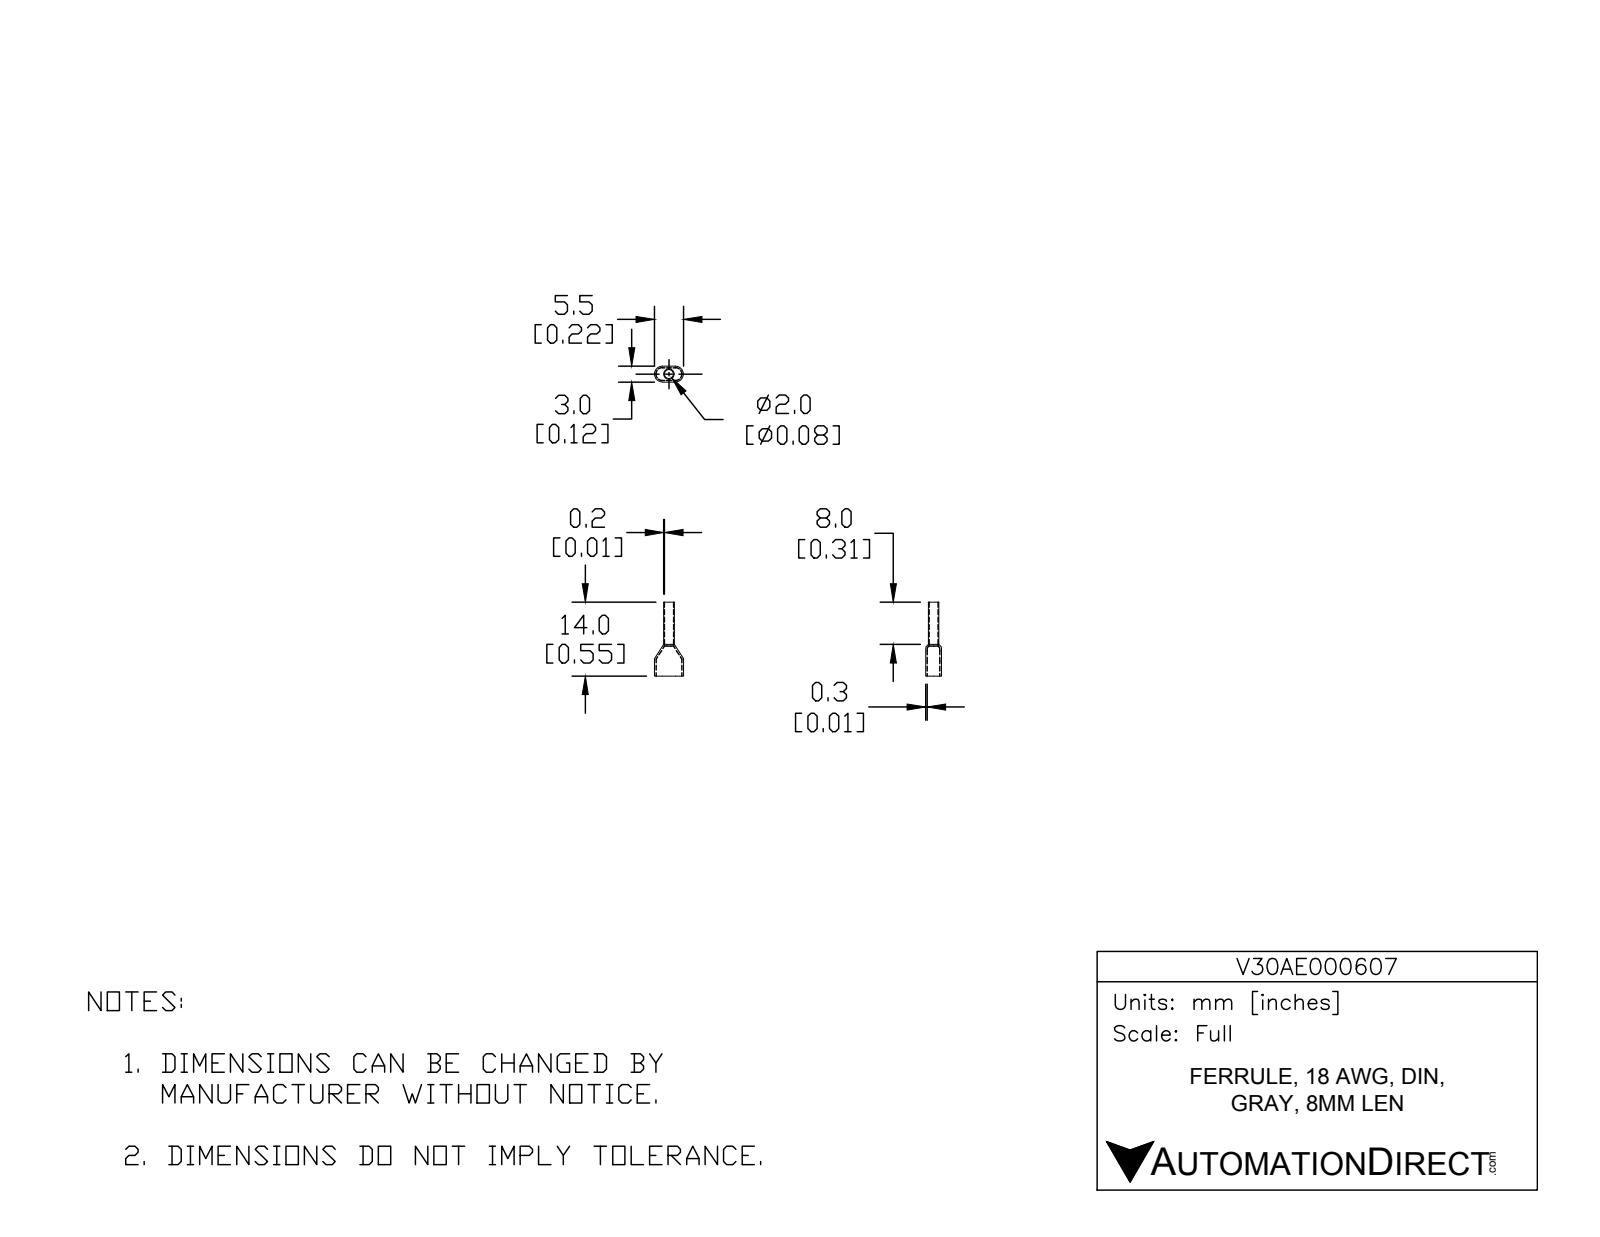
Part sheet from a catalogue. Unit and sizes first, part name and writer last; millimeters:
Units: millimetres
Overall size (bounding box): 14 × 5.5 × 3
Round holes (diameter × count): ⌀1.7 ×1
Round bosses / shafts (diameter × count): ⌀2 ×1
Partial cylindrical surfaces — rounded edges, fillets, slot ends (radius × count): R1.2 ×4, R1.5 ×4
Main face-to-face distances: 2.7, 3, 2.4, 6, 14, 8, 5.7, 8.3
Volume: 29 mm³ · Surface area: 246 mm²
Bodies: 2 solids, 36 faces (14 planar, 22 cylindrical, 0 other)
Part name (STEP PRODUCT): V30AE000607
STEP written by: SolidWorks 2017 (AUTOMOTIVE_DESIGN)
